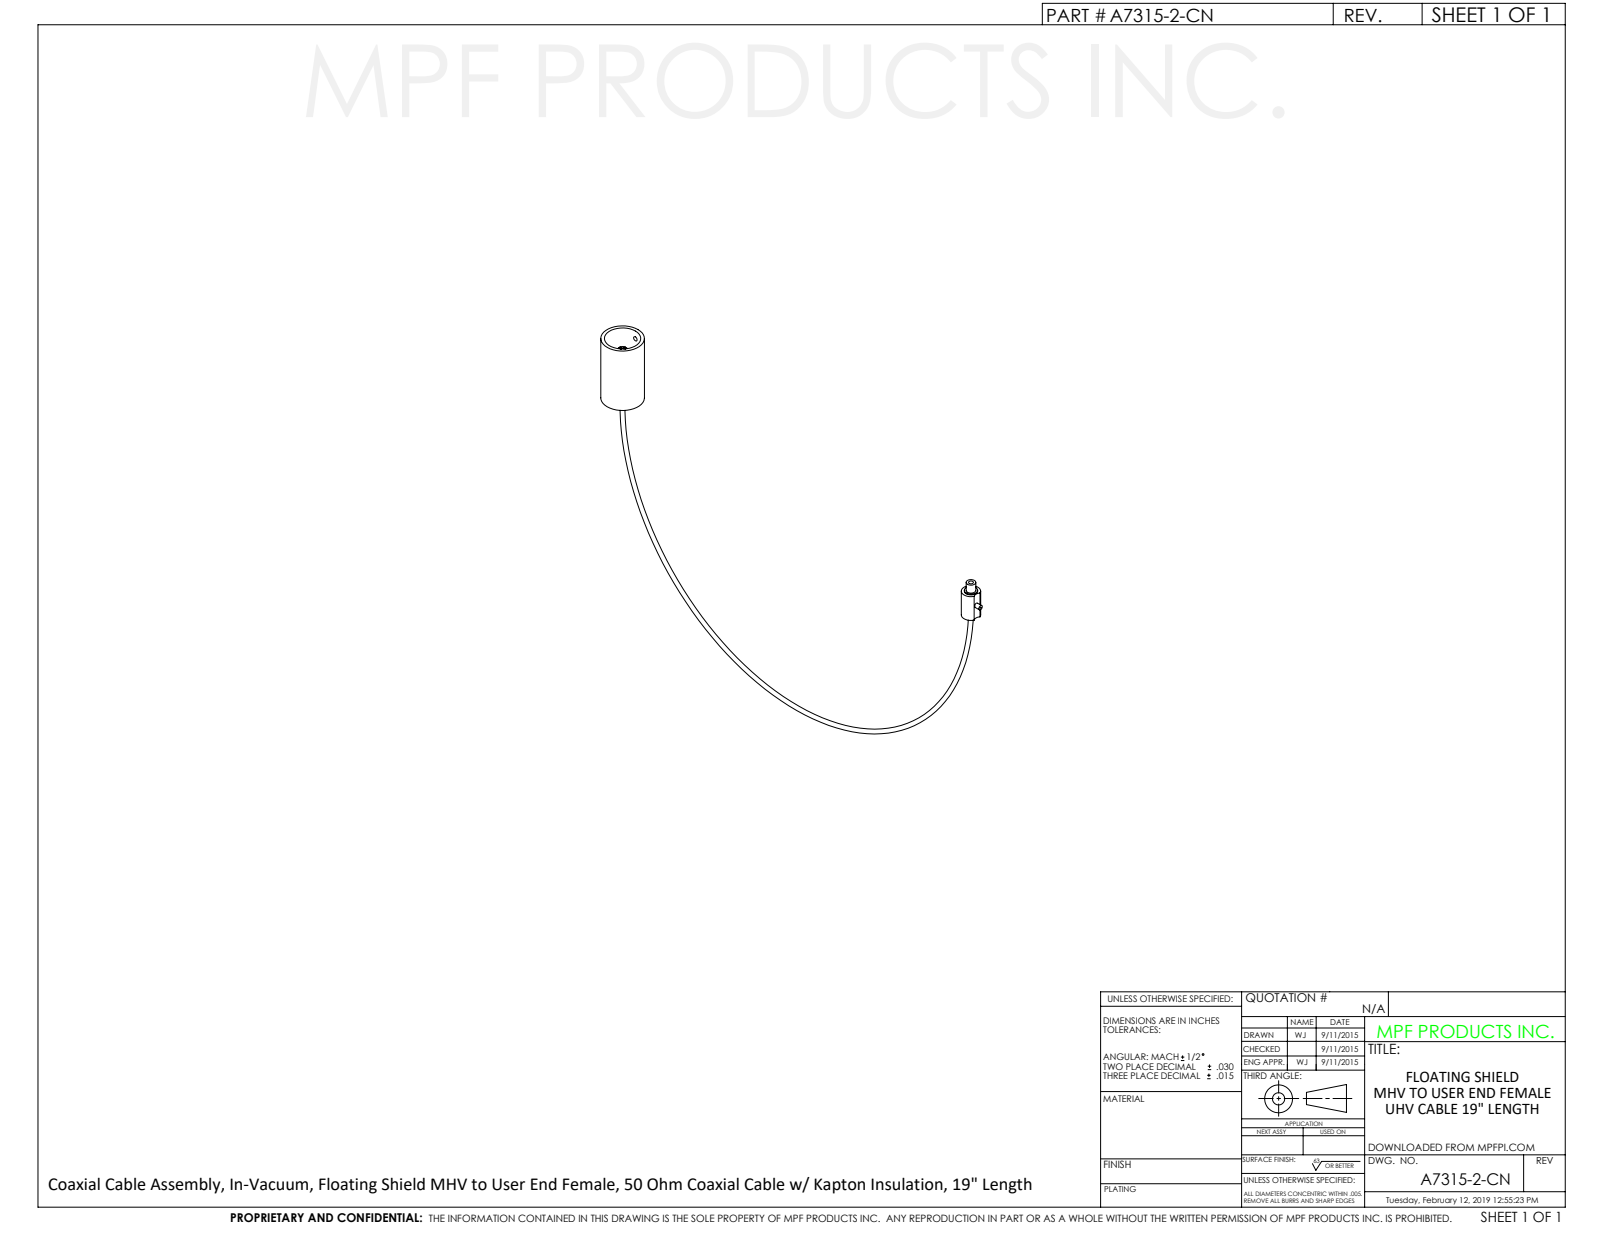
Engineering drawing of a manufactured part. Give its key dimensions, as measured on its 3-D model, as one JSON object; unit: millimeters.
{"part_name": "A7315-2-CN", "step_written_by": "SolidWorks 2012 (CONFIG_CONTROL_DESIGN)", "units": "millimeters", "bodies": {"solids": 1, "faces": 71, "planar": 30, "cylindrical": 36, "other": 5}, "overall_size": [282.4, 173.6, 25.4], "volume_mm3": 22990, "surface_area_mm2": 11040, "round_holes": [[2.5, 4], [0.6, 1], [5.1, 1], [19.1, 1]], "round_bosses_or_shafts": [[25.4, 1], [20.3, 1], [15.2, 1], [10.2, 1], [5.1, 1], [2.8, 1], [2.6, 1]], "partial_cylinders_radius": [[3.5, 1]], "face_to_face_distances": [10.1, 48.2, 38.1, 18.1, 8, 30.1, 0.5, 18.6, 8.5, 29.6], "hole_center_spacings": [8.9, 14.7, 258.1]}
